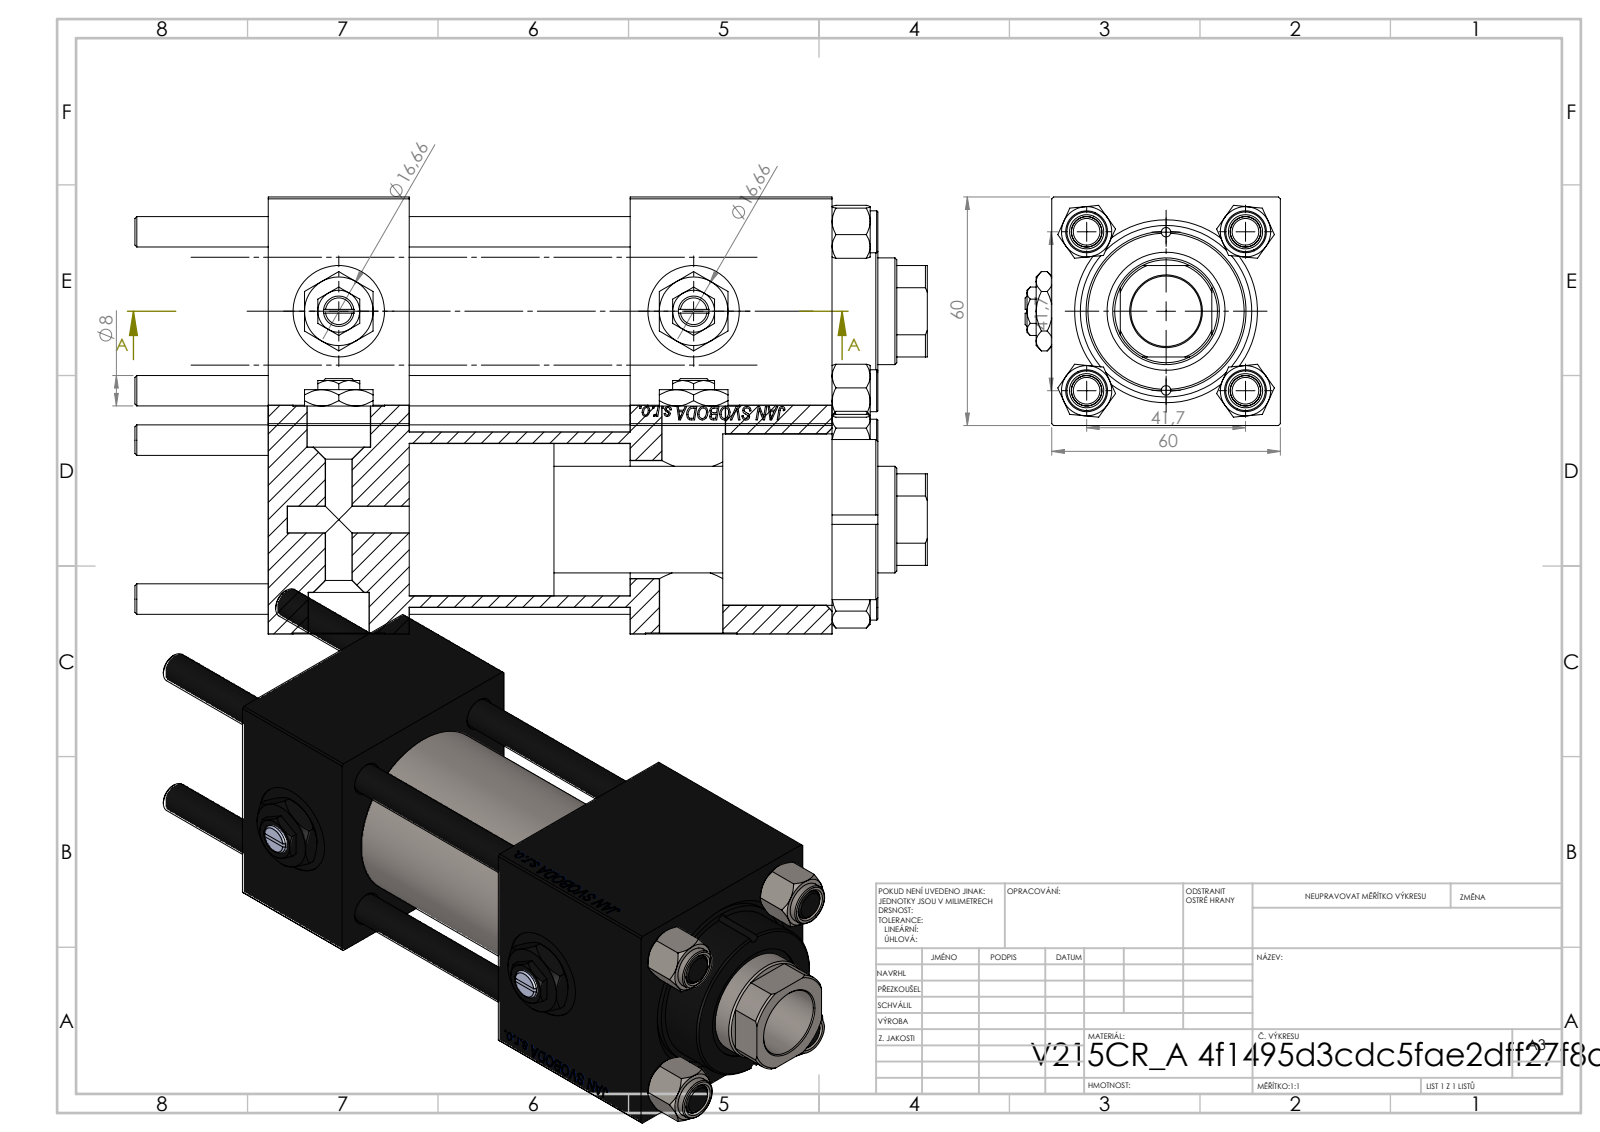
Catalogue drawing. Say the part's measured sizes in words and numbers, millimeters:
The part is named "NUT_M5; V215CR_BODY_A; CR025_012_A_0_G_A_G_M_020_+#_##_TYCINKA; V215_VC_A (+2 more)". Its 3-D file was written by "SolidWorks 2019 (CONFIG_CONTROL_DESIGN)". It is 13 solids with 1240 faces: 568 planar, 94 cylindrical and 578 other. Overall it measures 208 by 67 by 60 millimeters. Its volume is 431 595 cubic millimeters and its surface area 123 212 square millimeters. Round holes: 4 of diameter 8, 3 of diameter 16.66, 3 of diameter 24, 2 of diameter 2.5, 2 of diameter 7, 1 of diameter 16, 1 of diameter 18.5, 1 of diameter 28, 1 of diameter 31, 1 of diameter 40, 1 of diameter 45. Round bosses or shafts: 4 of diameter 11, 1 of diameter 46, 1 of diameter 42. Partial cylindrical surfaces (rounded edges, fillets, slot ends): 1 of radius 13.5. The main face-to-face distances are 60, 37, 58, 95, 53, 148, 111, 119.3, 82.3, 24.3. The hole center spacings are 20.85, 29.49, 41.7, 46.53, 20.75, 58.97, 0.66, 41.5.
